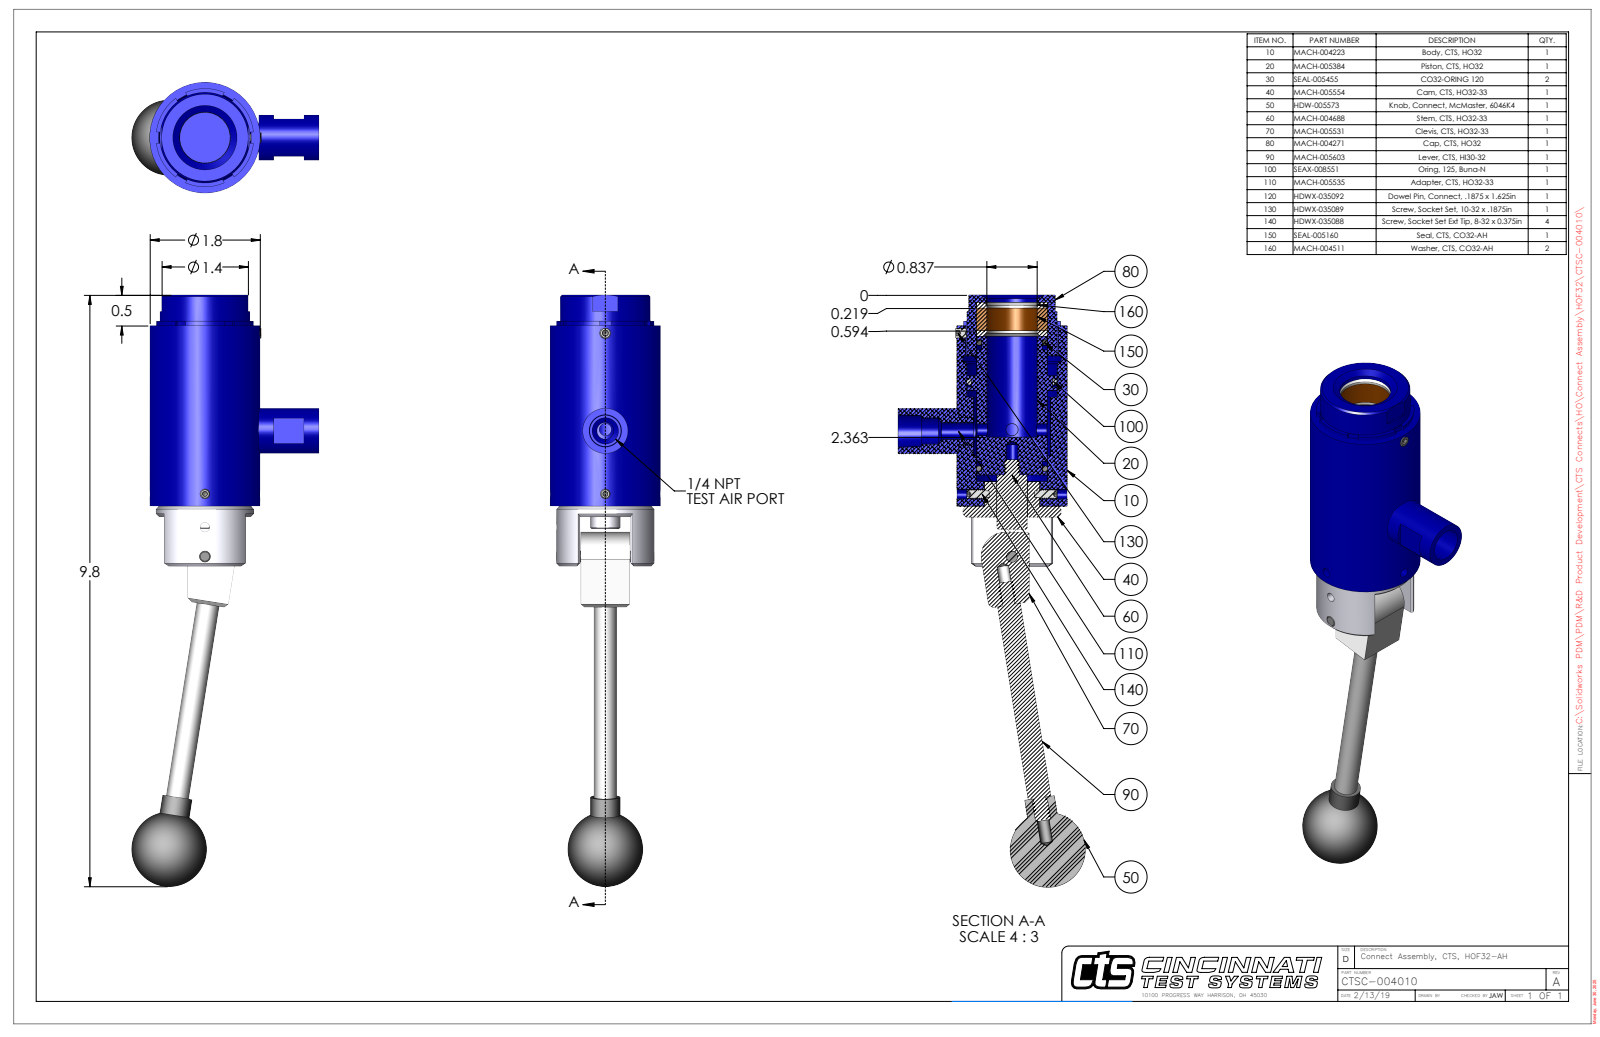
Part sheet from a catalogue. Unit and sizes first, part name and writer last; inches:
Units: inches
Overall size (bounding box): 9.837 × 3.109 × 1.832
Round holes (diameter × count): ⌀0.201 ×3, ⌀0.159 ×2, ⌀0.094 ×1, ⌀0.189 ×1, ⌀0.19 ×1, ⌀0.203 ×1, ⌀0.203 ×1, ⌀0.281 ×1, ⌀0.438 ×1, ⌀0.453 ×1, ⌀0.516 ×1, ⌀0.523 ×1
Round bosses / shafts (diameter × count): ⌀0.75 ×2, ⌀0.5 ×2, ⌀0.164 ×2, ⌀0.109 ×2, ⌀1.832 ×1, ⌀1.625 ×1, ⌀1.495 ×1, ⌀1.172 ×1
Partial cylindrical surfaces — rounded edges, fillets, slot ends (radius × count): R0.228 ×1, R0.4 ×1, R0.77 ×1, R0.811 ×1, R0.827 ×1
Main face-to-face distances: 0.014, 0.826, 0.178, 3, 0.094, 0.469, 0.375, 2.916, 3.291, 3.094
Hole centre spacings: 0.022, 0.488, 1.128, 1.603, 1.622, 1.625, 2.11, 2.75
Volume: 10.74 in³ · Surface area: 83.17 in²
Bodies: 14 solids, 530 faces (178 planar, 216 cylindrical, 136 other)
Part name (STEP PRODUCT): CTSC-004010
STEP written by: SolidWorks 2023 (AUTOMOTIVE_DESIGN)
